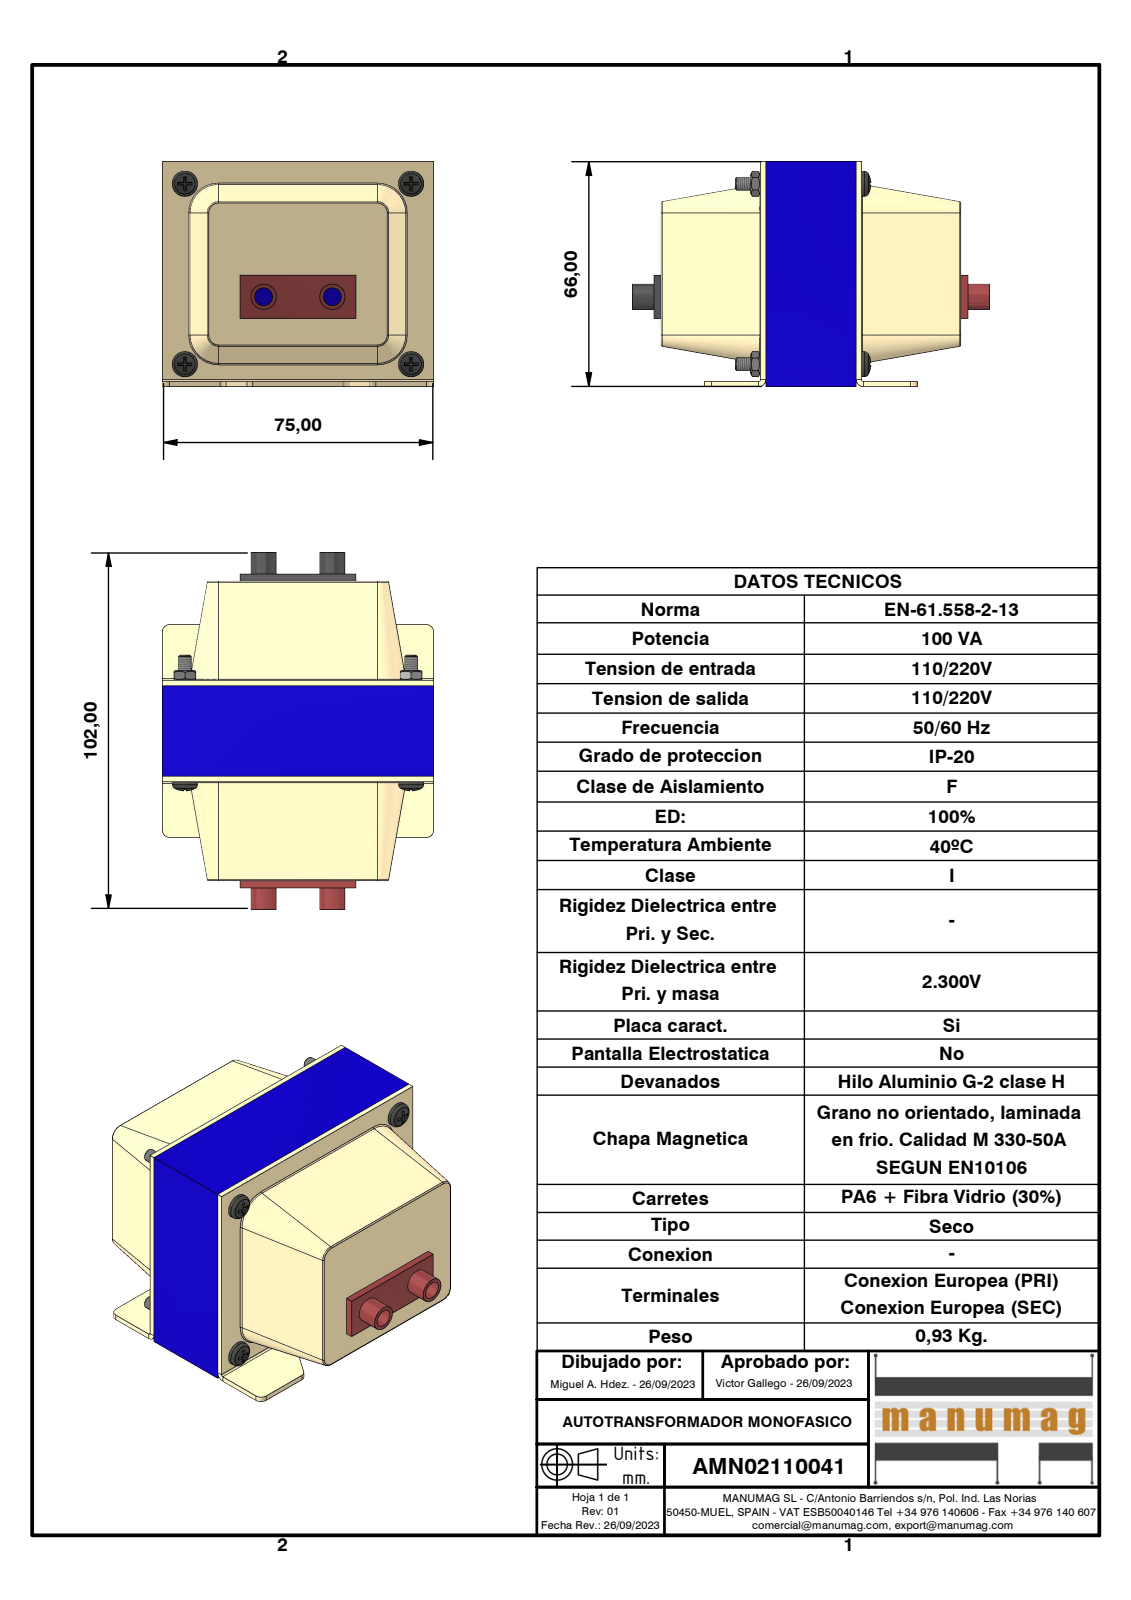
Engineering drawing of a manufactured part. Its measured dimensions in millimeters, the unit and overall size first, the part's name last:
Units: millimetres
Overall size (bounding box): 99 × 75 × 62.5
Round holes (diameter × count): ⌀2.85 ×4, ⌀3 ×4, ⌀4.5 ×4, ⌀5 ×2
Round bosses / shafts (diameter × count): ⌀3.5 ×4, ⌀3.18 ×4, ⌀7 ×2
Partial cylindrical surfaces — rounded edges, fillets, slot ends (radius × count): R0.38 ×16, R2 ×14, R0.5 ×2
Main face-to-face distances: 25, 1.5, 54, 27.5, 12.5, 53.58, 50, 62.5, 29, 63.43
Hole centre spacings: 28.67, 38.13, 44.83, 50, 51.4, 62.5, 80.04, 19
Volume: 111 042 mm³ · Surface area: 64 915 mm²
Bodies: 13 solids, 350 faces (162 planar, 64 cylindrical, 124 other)
Part name (STEP PRODUCT): AMN02110041; EI75 x 62,5 - 25 (RC25) Azul; TAPA RC25 RECEPTACULO; Receptaculo negro (+3 more)
STEP written by: Autodesk Inventor 2023 (AUTOMOTIVE_DESIGN)
